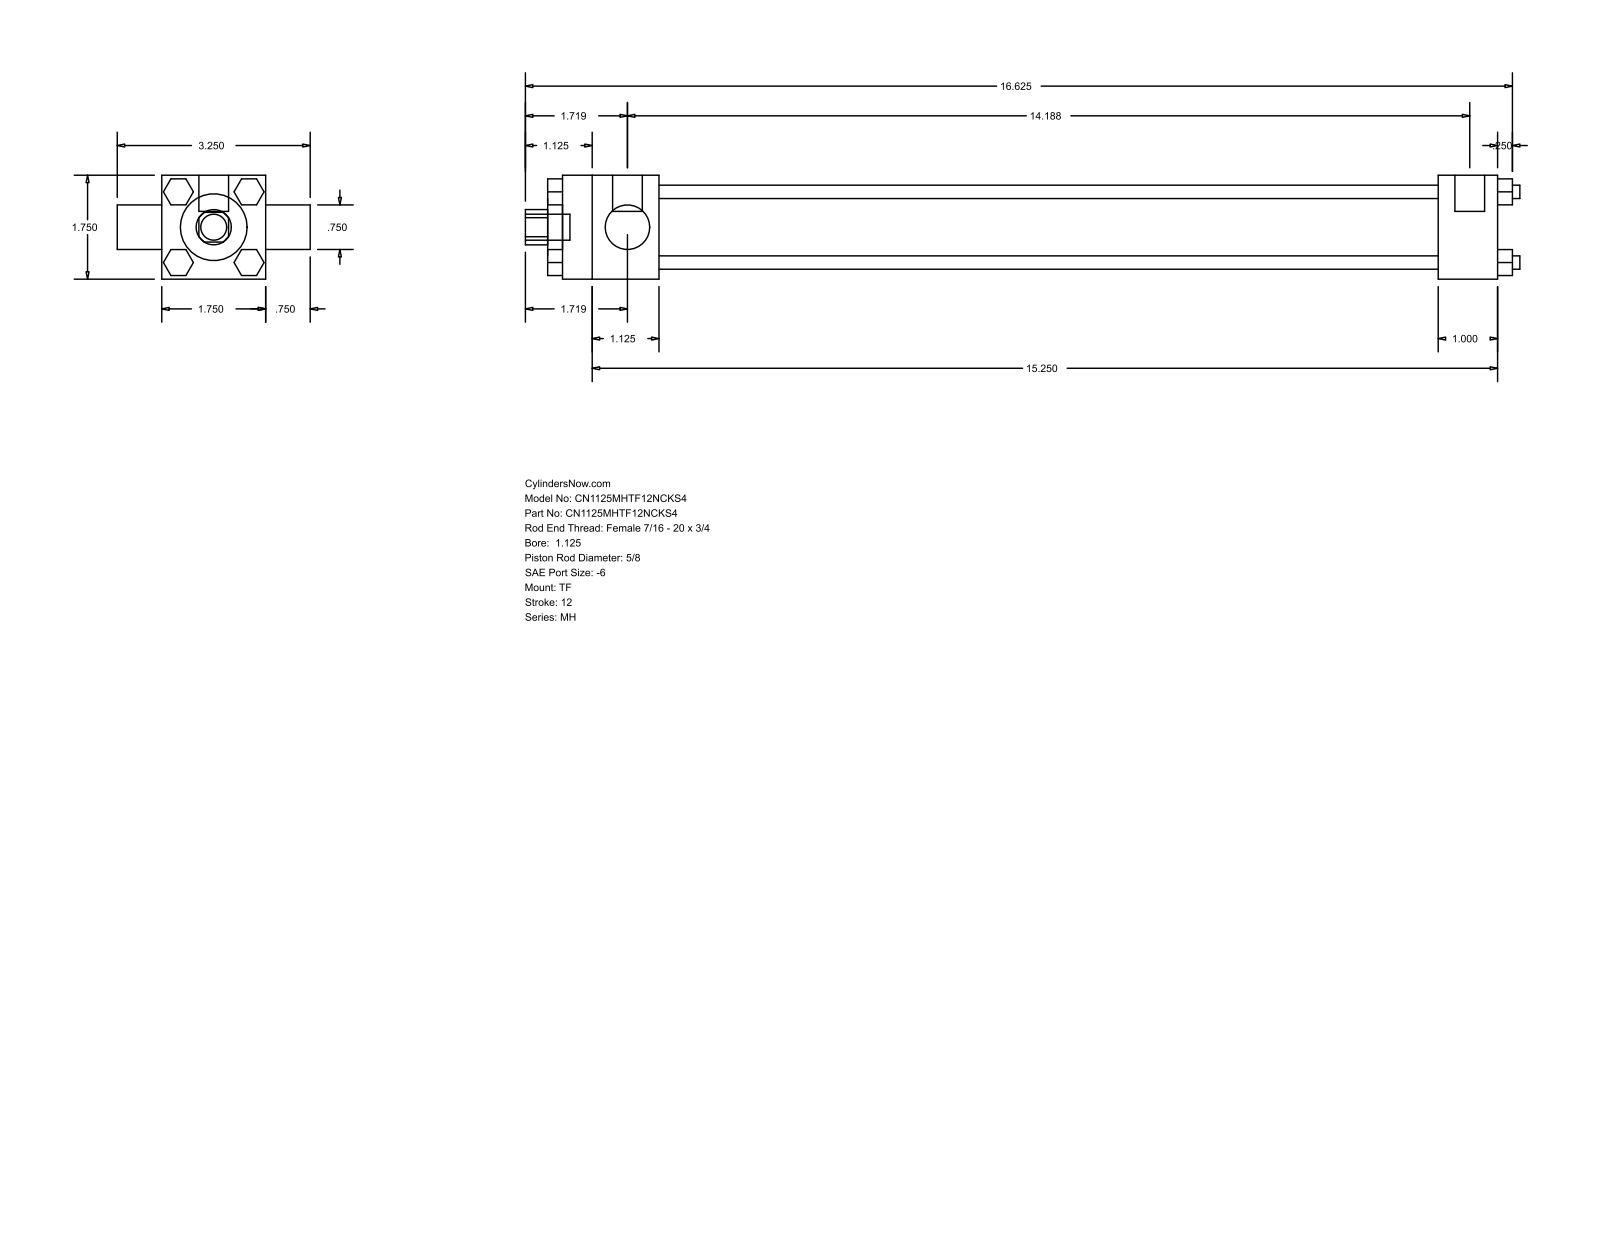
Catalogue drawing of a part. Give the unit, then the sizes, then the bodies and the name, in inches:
Units: inches
Overall size (bounding box): 16.75 × 3.25 × 1.75
Round holes (diameter × count): ⌀0.625 ×1, ⌀0.75 ×1, ⌀1.125 ×1, ⌀1.375 ×1
Round bosses / shafts (diameter × count): ⌀0.225 ×4, ⌀0.219 ×3, ⌀0.5 ×2, ⌀0.437 ×1
Partial cylindrical surfaces — rounded edges, fillets, slot ends (radius × count): R0.297 ×1
Main face-to-face distances: 1.75, 0.437, 13.125, 14.125, 1, 1.625, 14.75, 15.75, 1.875, 16
Bodies: 0 solids, 120 faces (92 planar, 28 cylindrical, 0 other)
Part name (STEP PRODUCT): MH_TF__0112_0.625
STEP written by: GSSL Pune (CONFIG_CONTROL_DESIGN)
